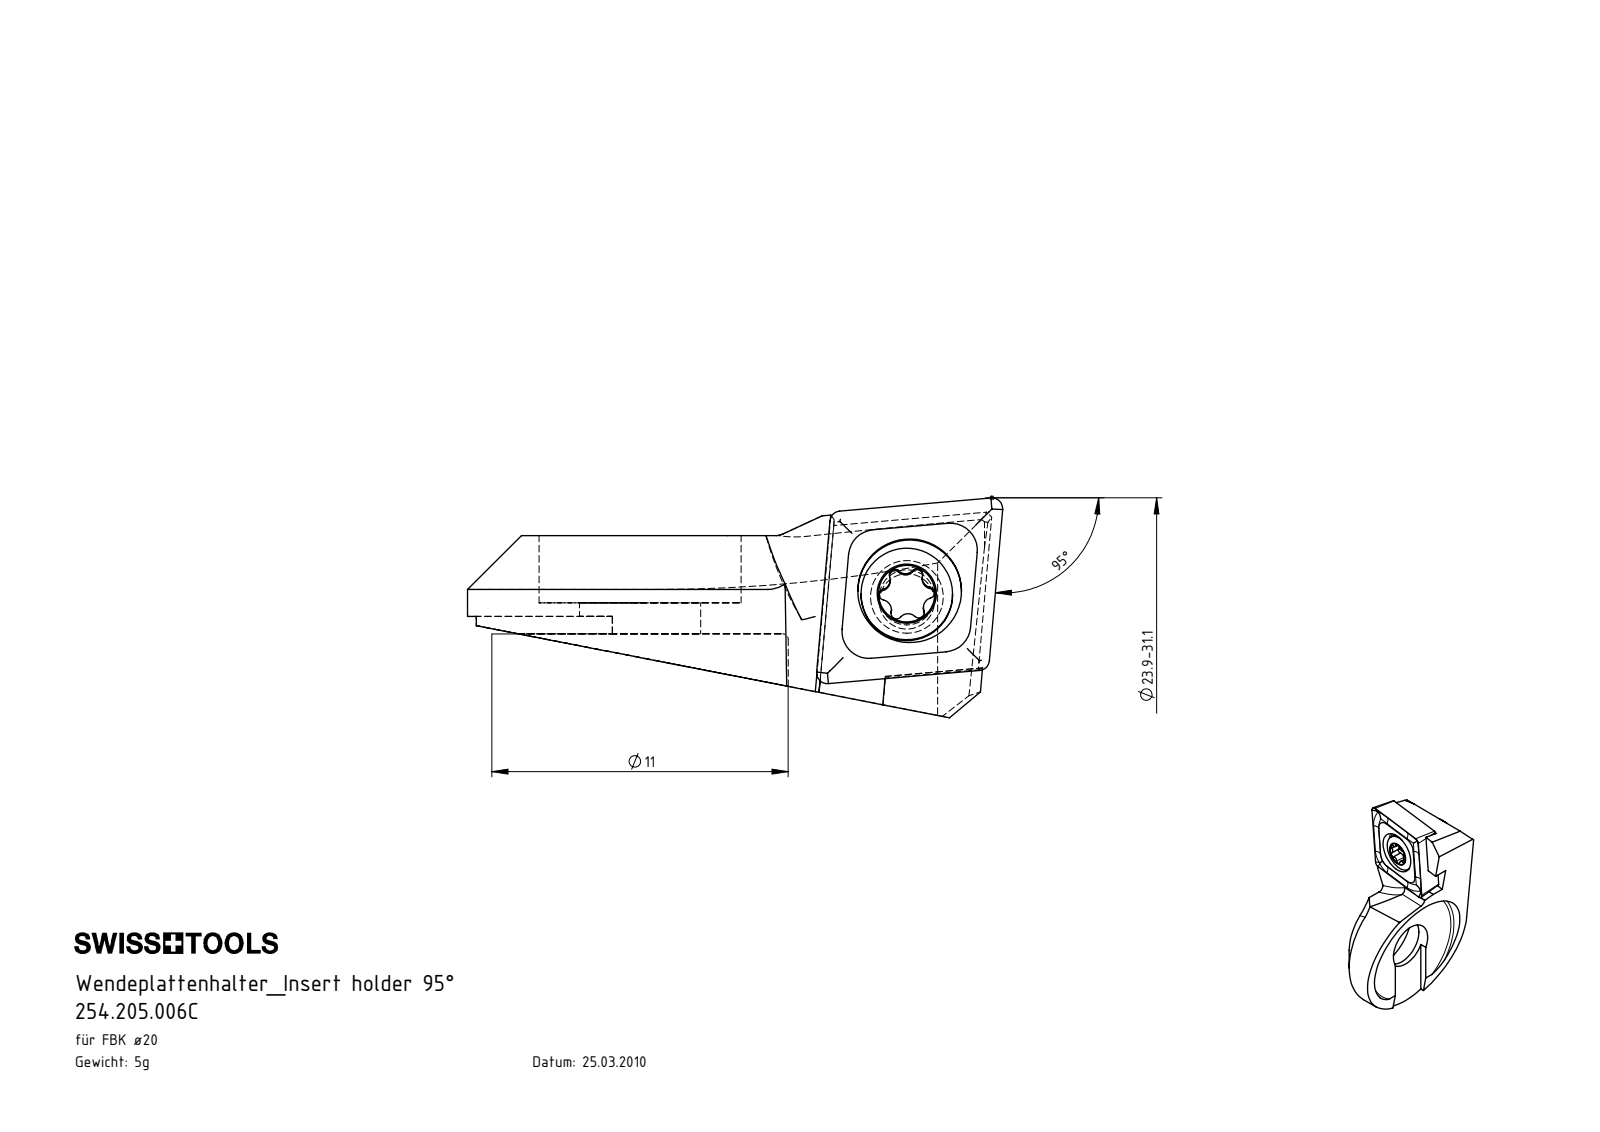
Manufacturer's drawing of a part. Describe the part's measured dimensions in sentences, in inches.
The part is named "254.205.006C; WCA-ER2.001.006_A; CCMT060204; F20-WCA.002.005_D_fertigbearbeitet". Its 3-D file was written by "SolidWorks 2017 (CONFIG_CONTROL_DESIGN)". It is 3 solids with 131 faces: 40 planar, 42 cylindrical and 49 other. Overall it measures 0.782 by 0.504 by 0.321 inches. Its volume is 0.034 cubic inches and its surface area 1.31 square inches. Round holes: 1 of diameter 0.081, 1 of diameter 0.11, 1 of diameter 0.152, 1 of diameter 0.177, 1 of diameter 0.295. Round bosses or shafts: 1 of diameter 0.134, 1 of diameter 0.098. Partial cylindrical surfaces (rounded edges, fillets, slot ends): 6 of radius 0.008, 5 of radius 0.014, 2 of radius 0.02, 2 of radius 0.197, 1 of radius 0.014, 1 of radius 0.217, 1 of radius 0.252, 1 of radius 0.394. The main face-to-face distances are 0.045, 0.098, 0.144, 0.118, 0.02, 0.026, 0.094, 0.043, 0.051, 0.039.
